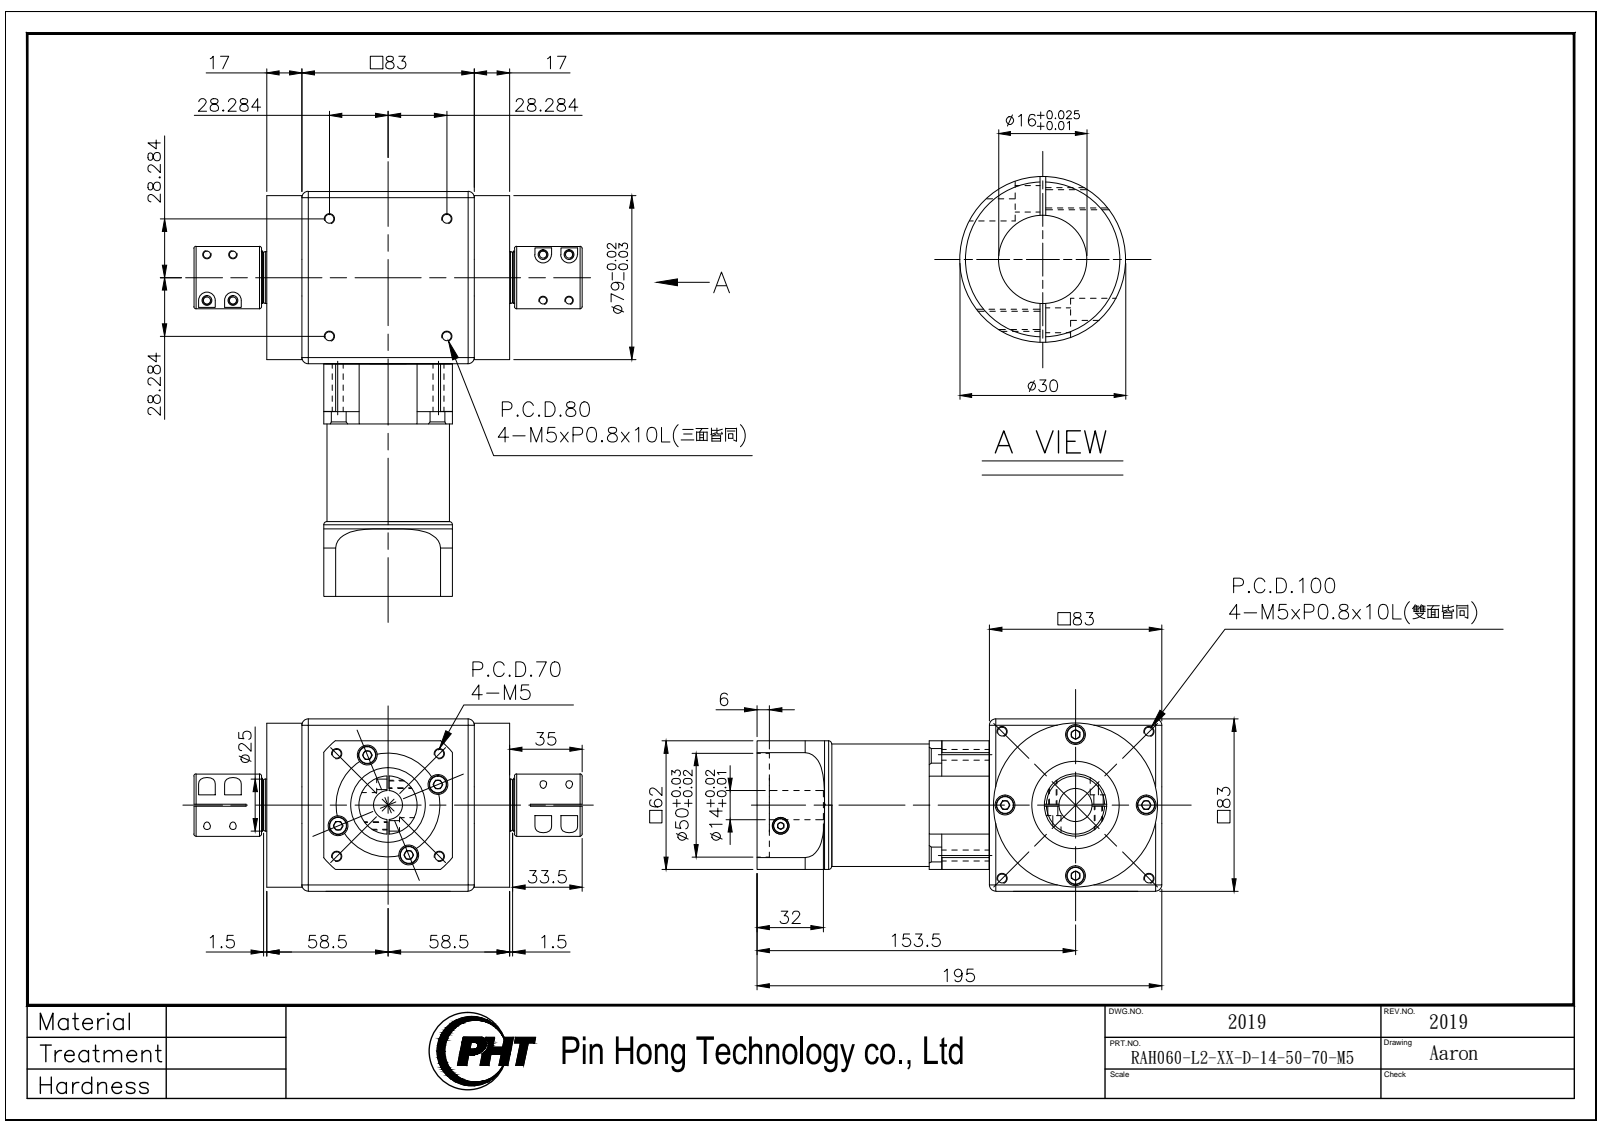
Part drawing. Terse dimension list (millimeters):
name: RAH060-L2-XX-D-14-50-70-M5_2019
written by: SolidWorks 2016 (AUTOMOTIVE_DESIGN)
unit: mm
bodies: 2 solids, 1006 faces (481 planar, 337 cylindrical, 188 other)
size: 195 × 187 × 83
volume: 1 070 000 mm³; area: 127 880 mm²
holes: 16× ⌀4.2, 8× ⌀4.1, 8× ⌀4.8, 8× ⌀5.2, 8× ⌀9.5, 4× ⌀5.5, 2× ⌀8, 1× ⌀14, 1× ⌀16, 1× ⌀16.6, 1× ⌀36
bosses: 12× ⌀8.5, 8× ⌀7.6, 8× ⌀7, 8× ⌀4, 1× ⌀79, 1× ⌀61.8, 1× ⌀59, 1× ⌀55
rounds: 8× R4, 4× R5, 1× R25, 1× R34, 1× R40, 1× R57.15
face distances: 83, 10.5, 72.5, 27.5, 62, 89.5, 17, 2, 117, 100
hole spacings: 53.15, 56.56, 4.99, 12.5, 14.82, 18.82, 22, 25.3
